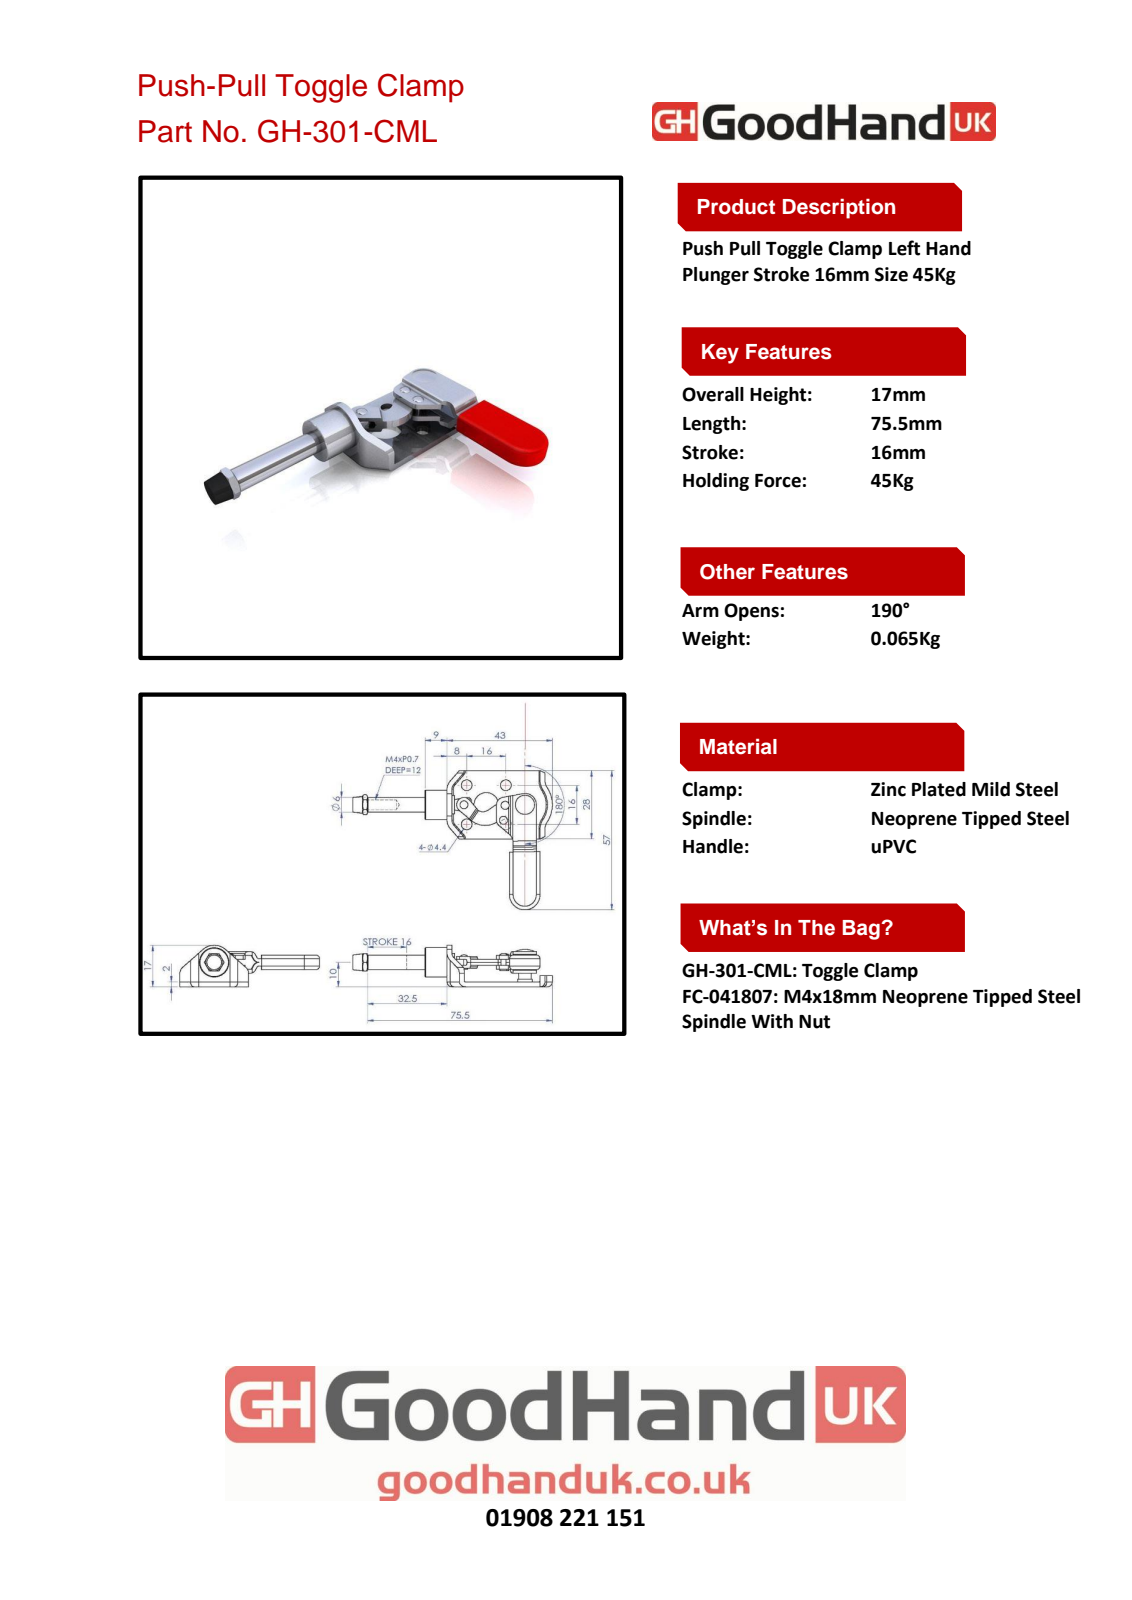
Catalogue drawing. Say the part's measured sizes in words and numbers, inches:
The part is named "GH-301-CML(簡化); 13605133-1^GH-301-CML(簡化); Group1^GH-301-CML(簡化); Group5^GH-301-CML(簡化) (+2 more)". Its 3-D file was written by "SolidWorks 2016 (AUTOMOTIVE_DESIGN)". It is 6 solids with 273 faces: 97 planar, 134 cylindrical and 42 other. Overall it measures 3.209 by 2.244 by 0.669 inches. Its volume is 0.486 cubic inches and its surface area 12.77 square inches. Round holes: 4 of diameter 0.173, 2 of diameter 0.059, 1 of diameter 0.13, 1 of diameter 0.161, 1 of diameter 0.236, 1 of diameter 0.295, 1 of diameter 0.394. Round bosses or shafts: 3 of diameter 0.118, 2 of diameter 0.157, 1 of diameter 0.472, 1 of diameter 0.236, 1 of diameter 0.228, 1 of diameter 0.197, 1 of diameter 0.059. Partial cylindrical surfaces (rounded edges, fillets, slot ends): 8 of radius 0.024, 8 of radius 0.03, 6 of radius 0.079, 6 of radius 0.118, 4 of radius 0.02, 4 of radius 0.059, 2 of radius 0.028, 2 of radius 0.039. The main face-to-face distances are 0.079, 0.22, 0.059, 0.232, 0.165, 0.161, 0.433, 0.071, 0.067, 0.055. The hole center spacings are 0.445, 0.63, 0.318, 0.743, 0.891, 0.303, 0.307, 0.324.
